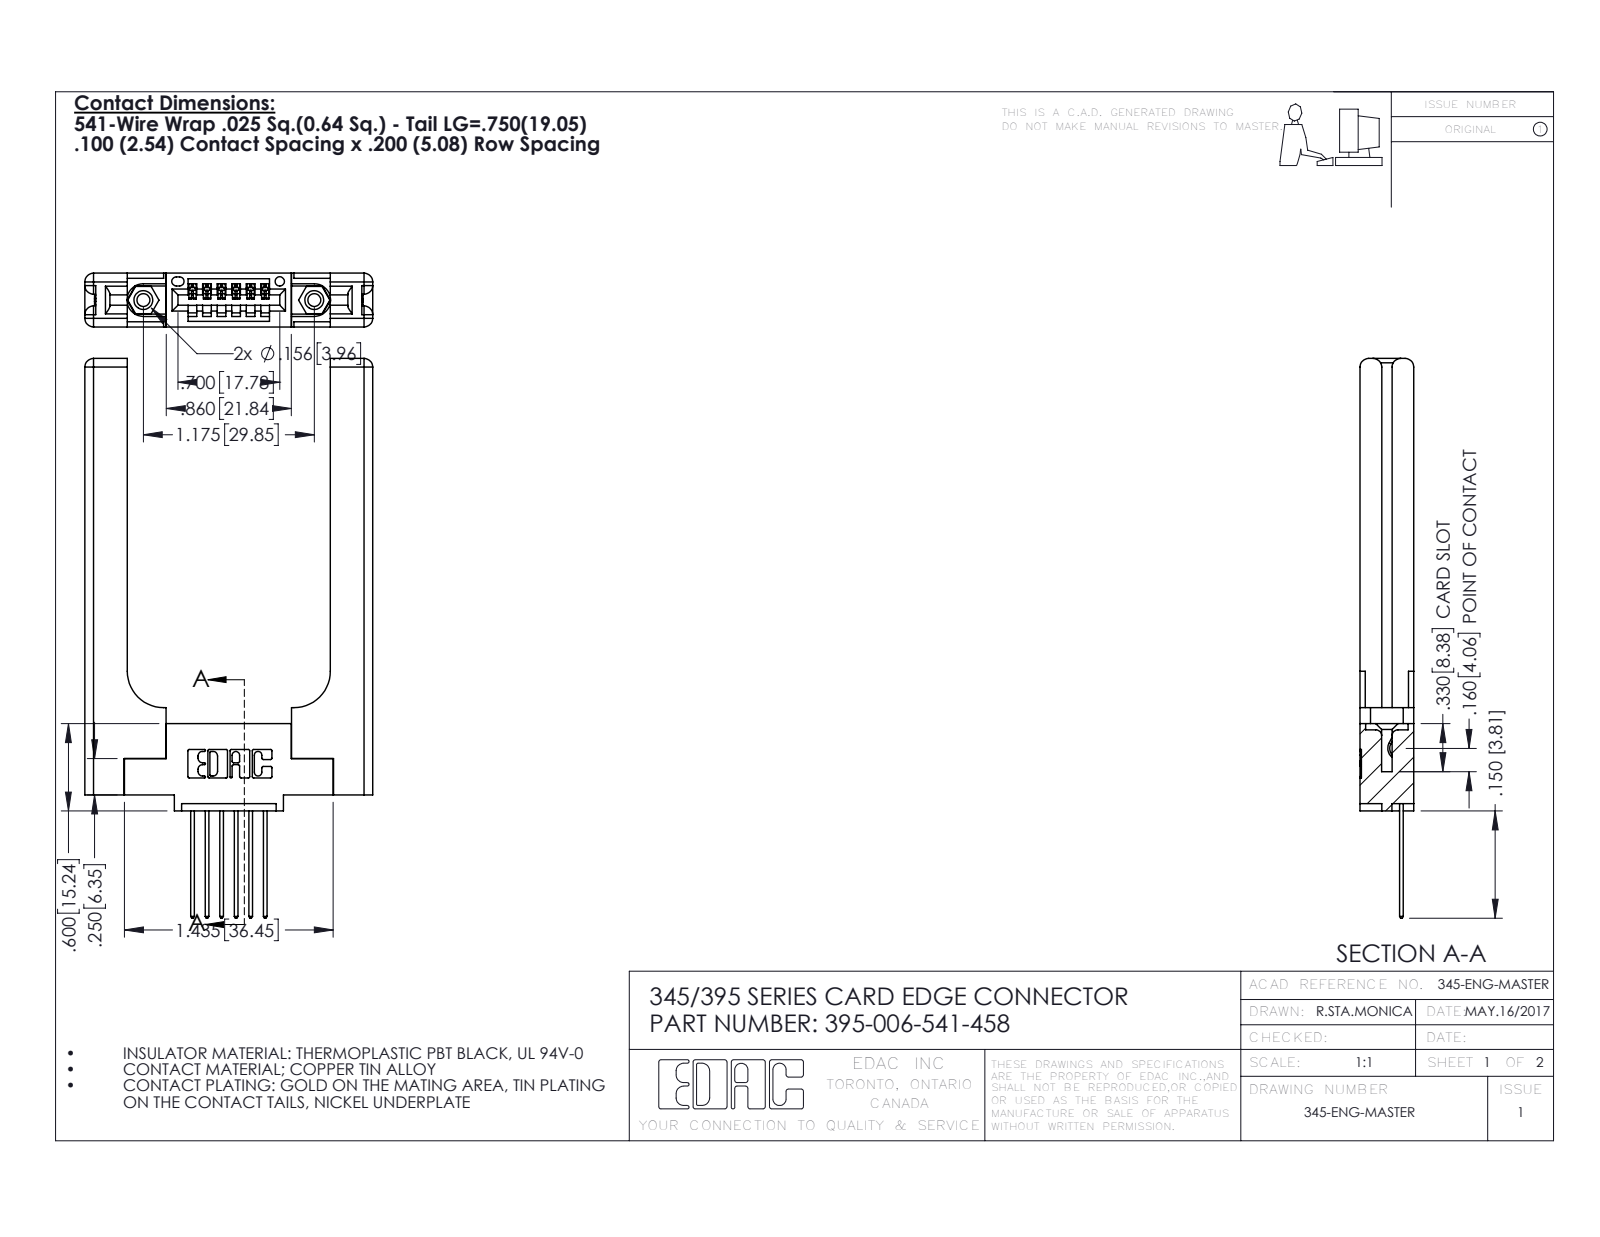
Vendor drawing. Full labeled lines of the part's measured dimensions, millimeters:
Part name (STEP PRODUCT): 345-220-058_345-220-058; 395-006-541-458; 345-292-001_345-293-141; 345 Part_0.110 Offset - 0.156 Dia-TH (+1 more)
STEP written by: SolidWorks 2016 (CONFIG_CONTROL_DESIGN)
Units: millimetres
Bodies: 11 solids, 734 faces (472 planar, 202 cylindrical, 60 other)
Overall size (bounding box): 97.7 × 50.3 × 9.4
Volume: 12 900 mm³ · Surface area: 10 900 mm²
Round holes (diameter × count): ⌀2.3 ×2, ⌀3.2 ×2, ⌀4 ×2, ⌀1.6 ×1
Round bosses / shafts (diameter × count): ⌀3.9 ×2
Partial cylindrical surfaces — rounded edges, fillets, slot ends (radius × count): R0.3 ×22, R1.5 ×16, R0.2 ×12, R0.3 ×12, R0.2 ×6, R0.8 ×6, R0.7 ×3, R0.8 ×2
Main face-to-face distances: 9.4, 3.8, 5.6, 1.8, 3.8, 2, 7.6, 35.5, 1.8, 7.4
Hole centre spacings: 6.9, 24, 29.8
